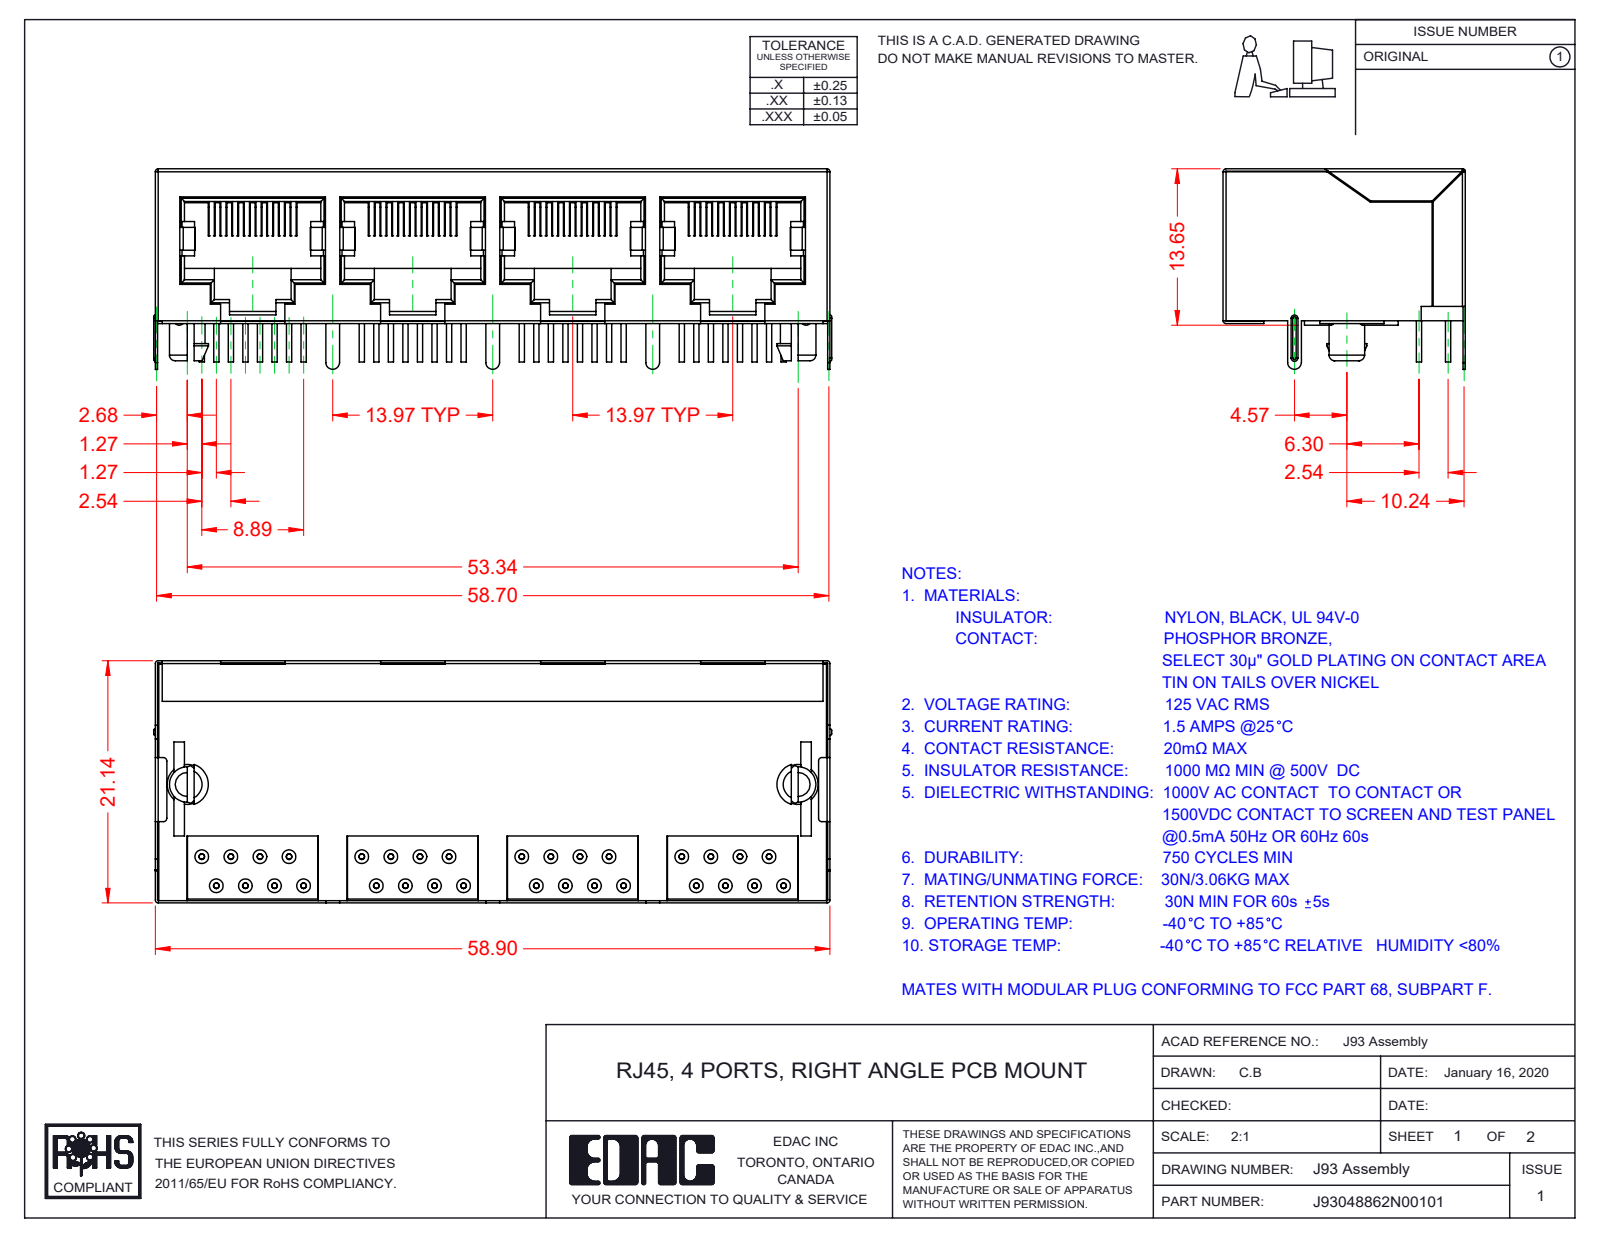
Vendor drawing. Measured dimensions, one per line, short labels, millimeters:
name: 93 Insulator; 93 Contact Lock; 93 Contacts; RJ93048862N00101 (+1 more)
written by: SolidWorks 2016 (CONFIG_CONTROL_DESIGN)
unit: mm
bodies: 38 solids, 2070 faces (1065 planar, 665 cylindrical, 340 other)
size: 59.2 × 21.14 × 17.5
volume: 9 684 mm³; area: 21 056 mm²
holes: 32× ⌀0.46
bosses: 128× ⌀0.46, 2× ⌀3.1
rounds: 22× R0.3, 22× R0.5, 16× R0.19, 11× R0.25, 4× R0.15, 4× R0.6, 2× R0.4, 2× R0.46
face distances: 0.8, 12.25, 12.2, 1, 0.75, 13.25, 13.05, 1.05, 0.85, 13
hole spacings: 2.84, 2.54, 13.97, 15.45, 12.95, 4.58, 16.51, 11.43
